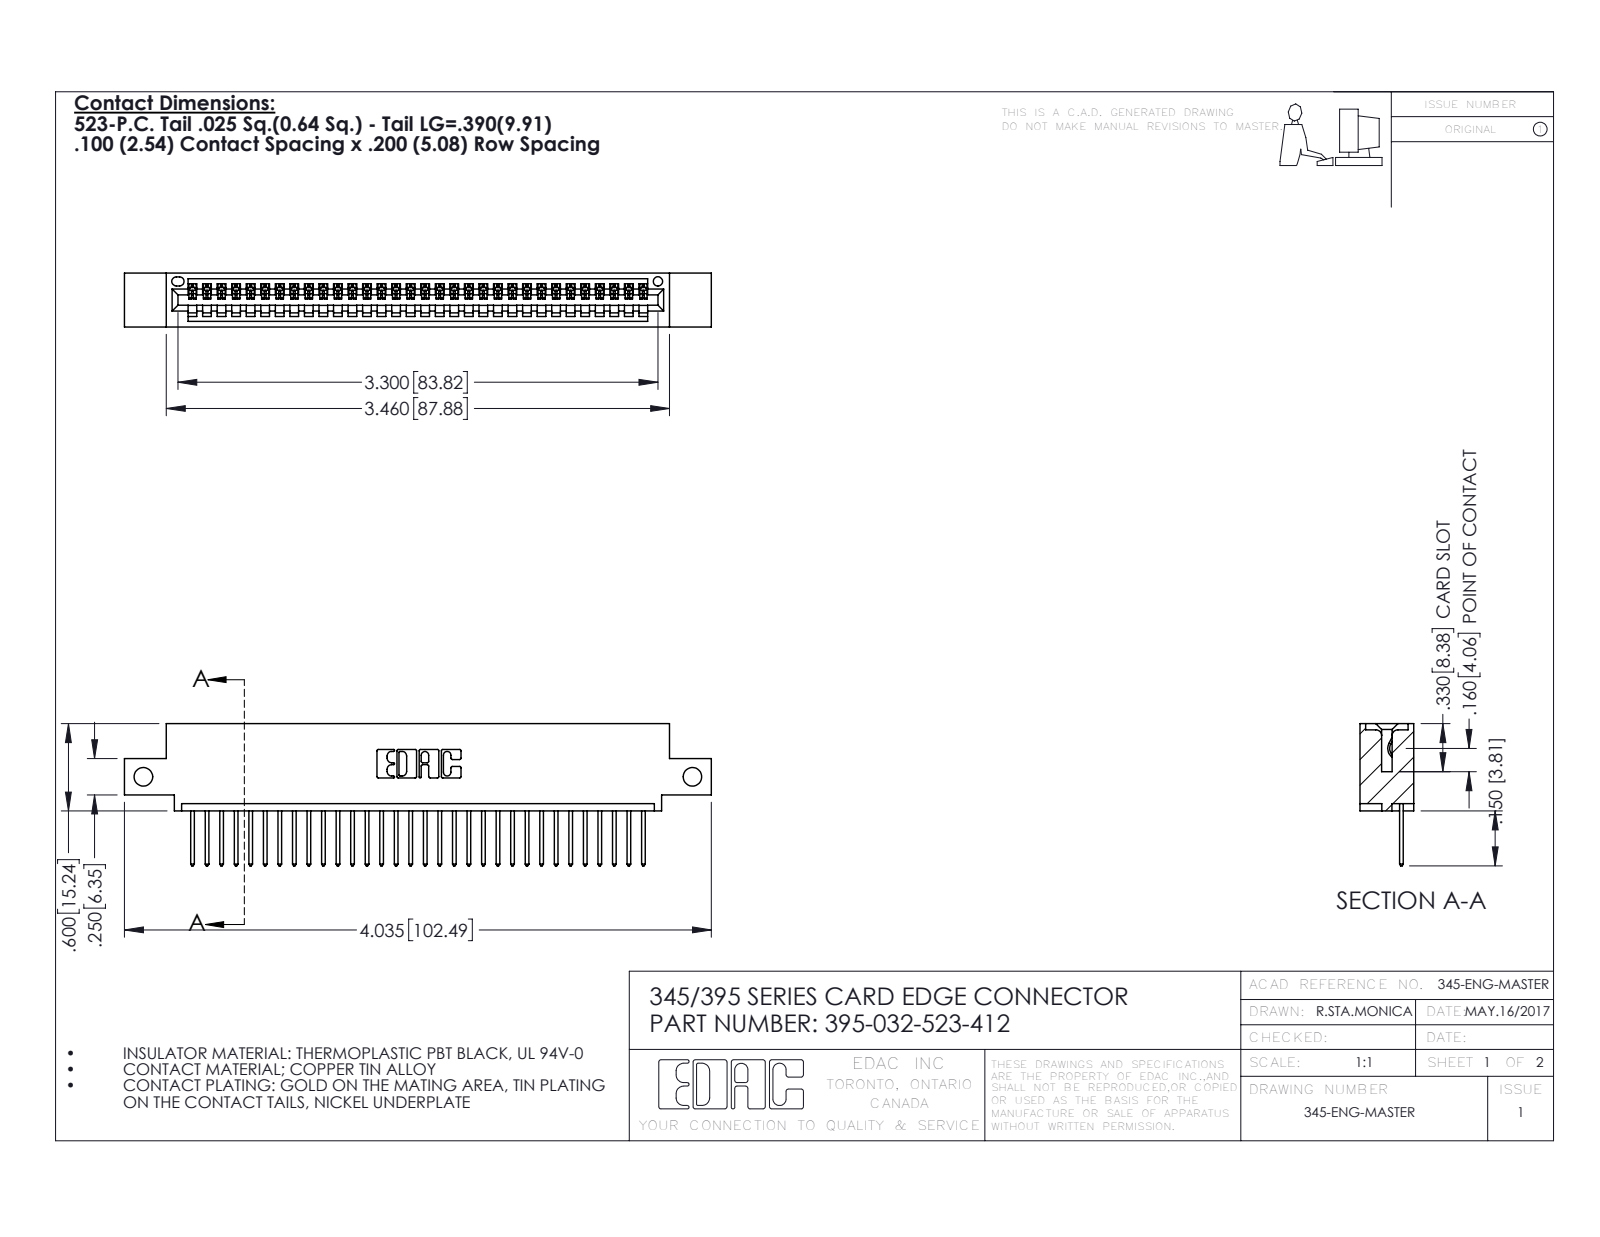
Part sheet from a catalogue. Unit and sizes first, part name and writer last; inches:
Units: inches
Overall size (bounding box): 4.035 × 0.977 × 0.37
Round holes (diameter × count): ⌀0.128 ×2, ⌀0.064 ×1
Partial cylindrical surfaces — rounded edges, fillets, slot ends (radius × count): R0.006 ×64, R0.01 ×64, R0.01 ×22, R0.007 ×6, R0.031 ×6, R0.026 ×3, R0.031 ×2, R0.04 ×2
Main face-to-face distances: 0.072, 0.298, 0.37, 0.2, 0.098, 0.272, 0.025, 0.225, 0.149, 0.072
Hole centre spacings: 3.775
Volume: 0.578 in³ · Surface area: 19.28 in²
Bodies: 33 solids, 1986 faces (1364 planar, 622 cylindrical, 0 other)
Part name (STEP PRODUCT): 345 Part_0.110 Offset - Side Mount; 395-032-523-412; 345-292-001_345-293-123
STEP written by: SolidWorks 2016 (CONFIG_CONTROL_DESIGN)
